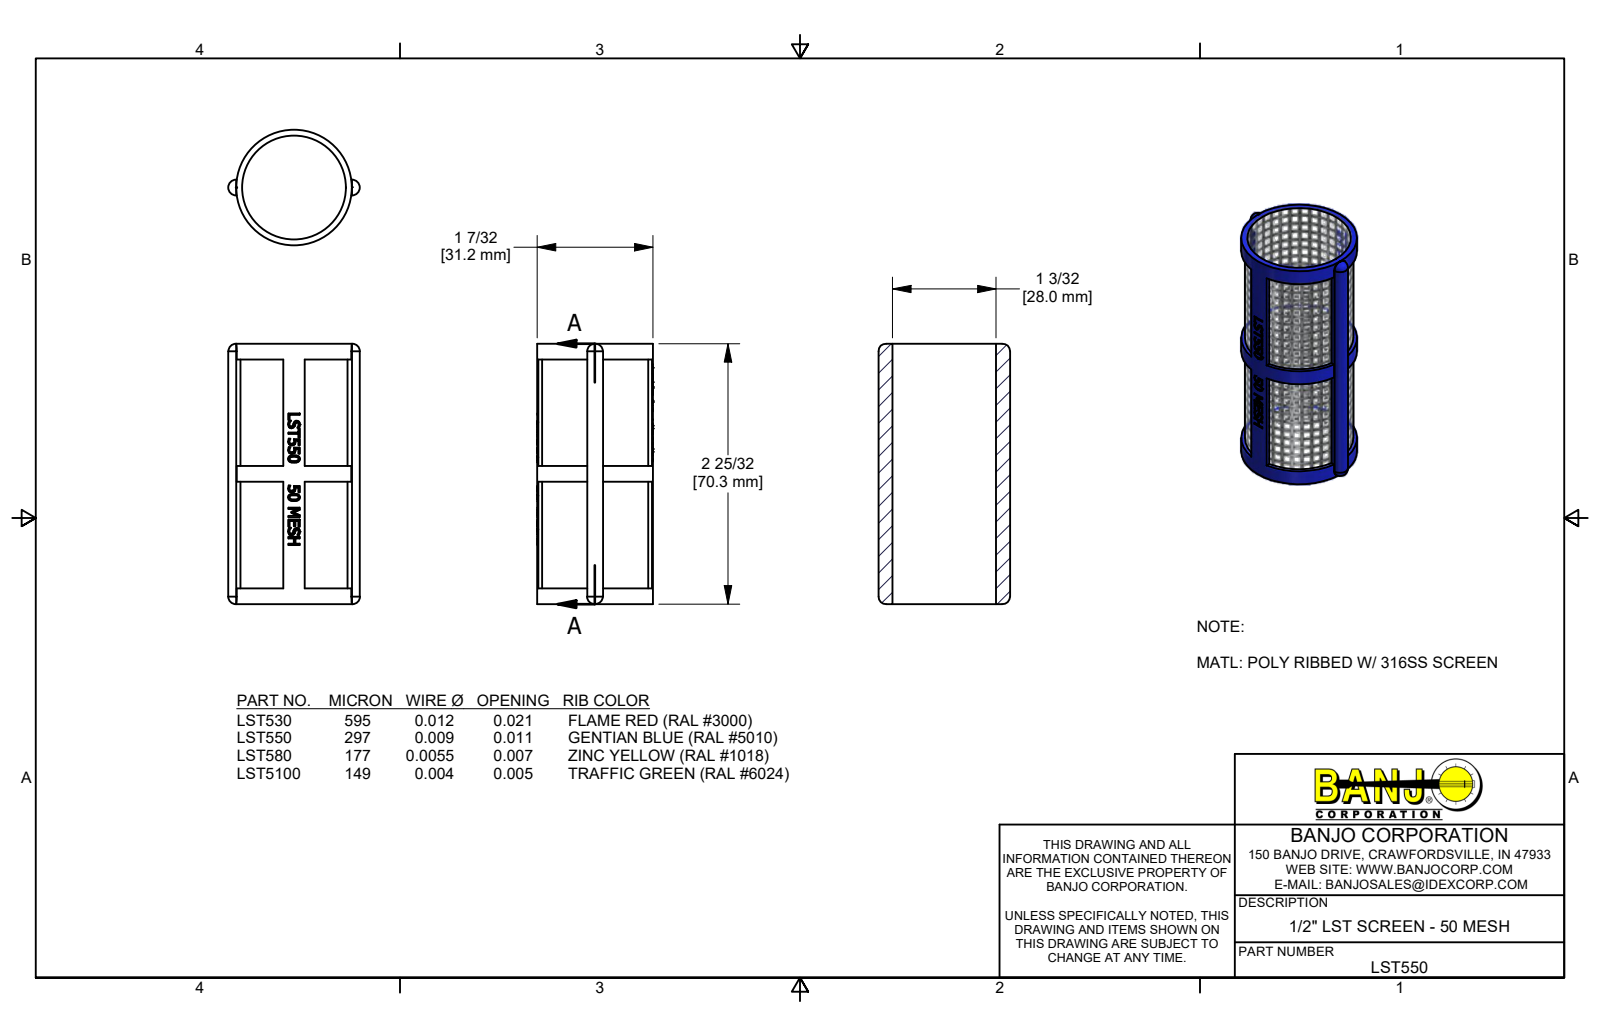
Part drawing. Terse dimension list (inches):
name: LST550
written by: Autodesk Inventor 2019 (AUTOMOTIVE_DESIGN)
unit: in
bodies: 1 solid, 397 faces (235 planar, 51 cylindrical, 111 other)
size: 2.766 × 1.398 × 1.23
volume: 0.45 in³; area: 22.24 in²
holes: 1× ⌀1.101
bosses: 1× ⌀1.23
rounds: 4× R0.08, 2× R0.084, 1× R0.576, 1× R0.595
face distances: 0.168, 2.766, 1.299, 2.598, 1.299, 0.168, 0.227, 1.467, 1.467, 1.131
